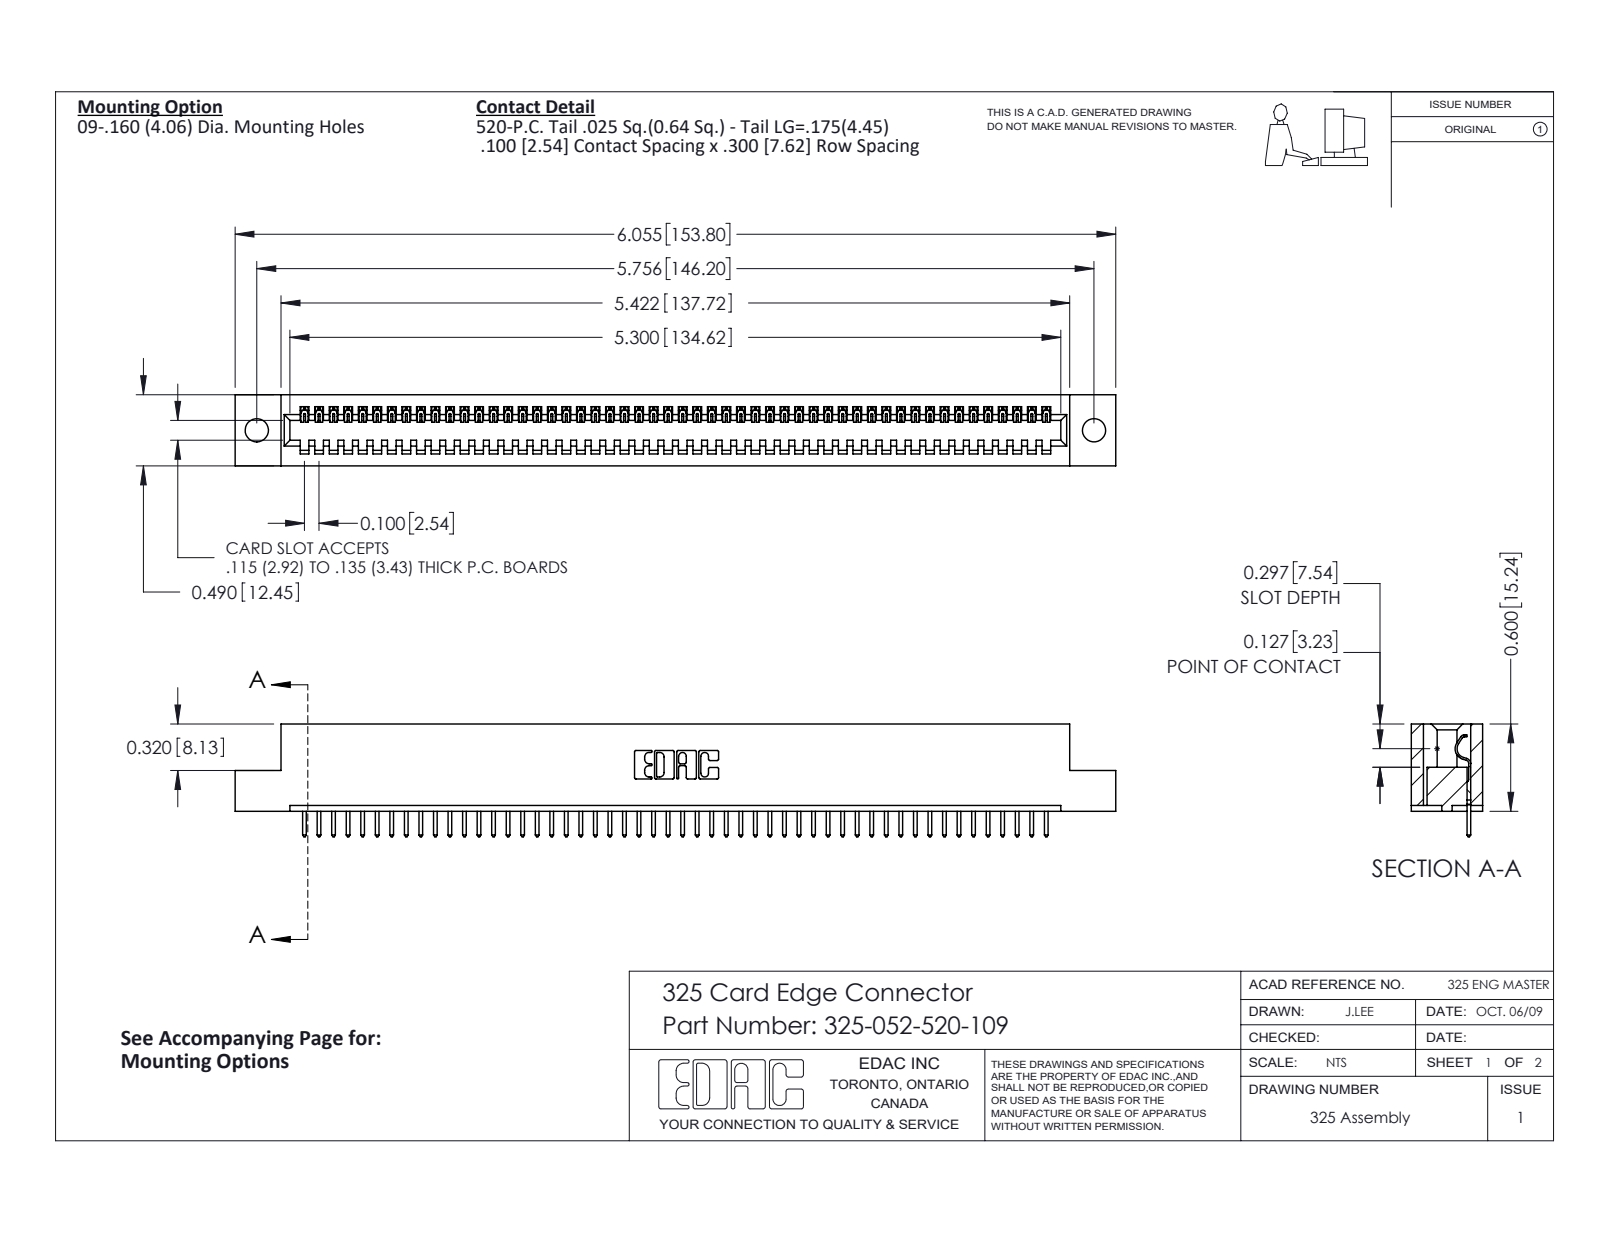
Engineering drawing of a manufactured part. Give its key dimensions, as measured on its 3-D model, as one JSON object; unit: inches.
{"part_name": "325-292-001_325-293-120; 325 Part_.160 TH; 325-052-520-109", "step_written_by": "SolidWorks 2016 (CONFIG_CONTROL_DESIGN)", "units": "inches", "bodies": {"solids": 53, "faces": 3130, "planar": 2254, "cylindrical": 876, "other": 0}, "overall_size": [6.055, 0.775, 0.49], "volume_in3": 1.174, "surface_area_in2": 31.83, "round_holes": [[0.16, 2]], "partial_cylinders_radius": [[0.006, 104], [0.01, 104], [0.01, 22], [0.007, 6], [0.031, 6], [0.026, 3], [0.014, 1], [0.022, 1]], "face_to_face_distances": [0.083, 0.407, 0.49, 0.3, 0.107, 0.383, 0.025, 0.325, 0.56, 0.263], "hole_center_spacings": [5.756]}
